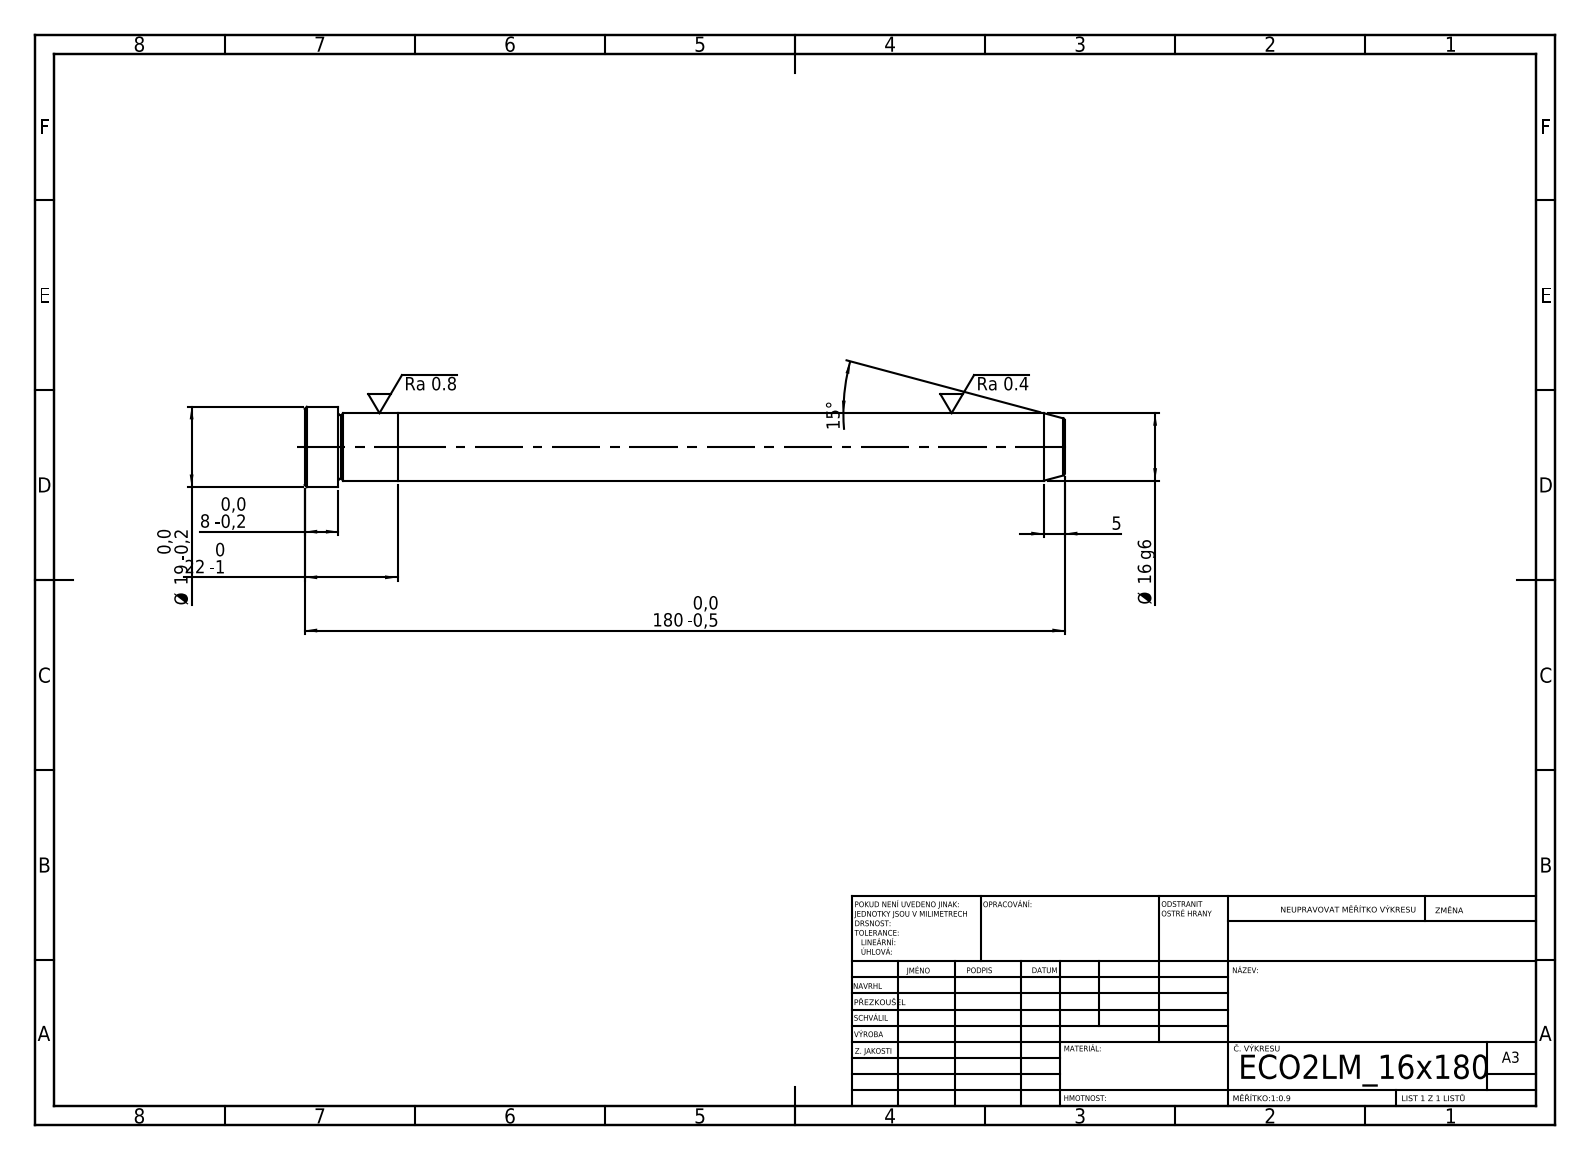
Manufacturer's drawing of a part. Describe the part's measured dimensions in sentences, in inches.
Its 3-D file was written by "SolidWorks 2019 (CONFIG_CONTROL_DESIGN)". It is 2 solids with 21 faces: 5 planar, 6 cylindrical and 10 other. Overall it measures 7.087 by 0.748 by 0.748 inches. Its volume is 2.237 cubic inches and its surface area 15.53 square inches. Round bosses or shafts: 1 of diameter 0.748, 1 of diameter 0.63. The main face-to-face distances are 0.866, 6.22, 7.087, 6.772, 0.551, 0.315.
